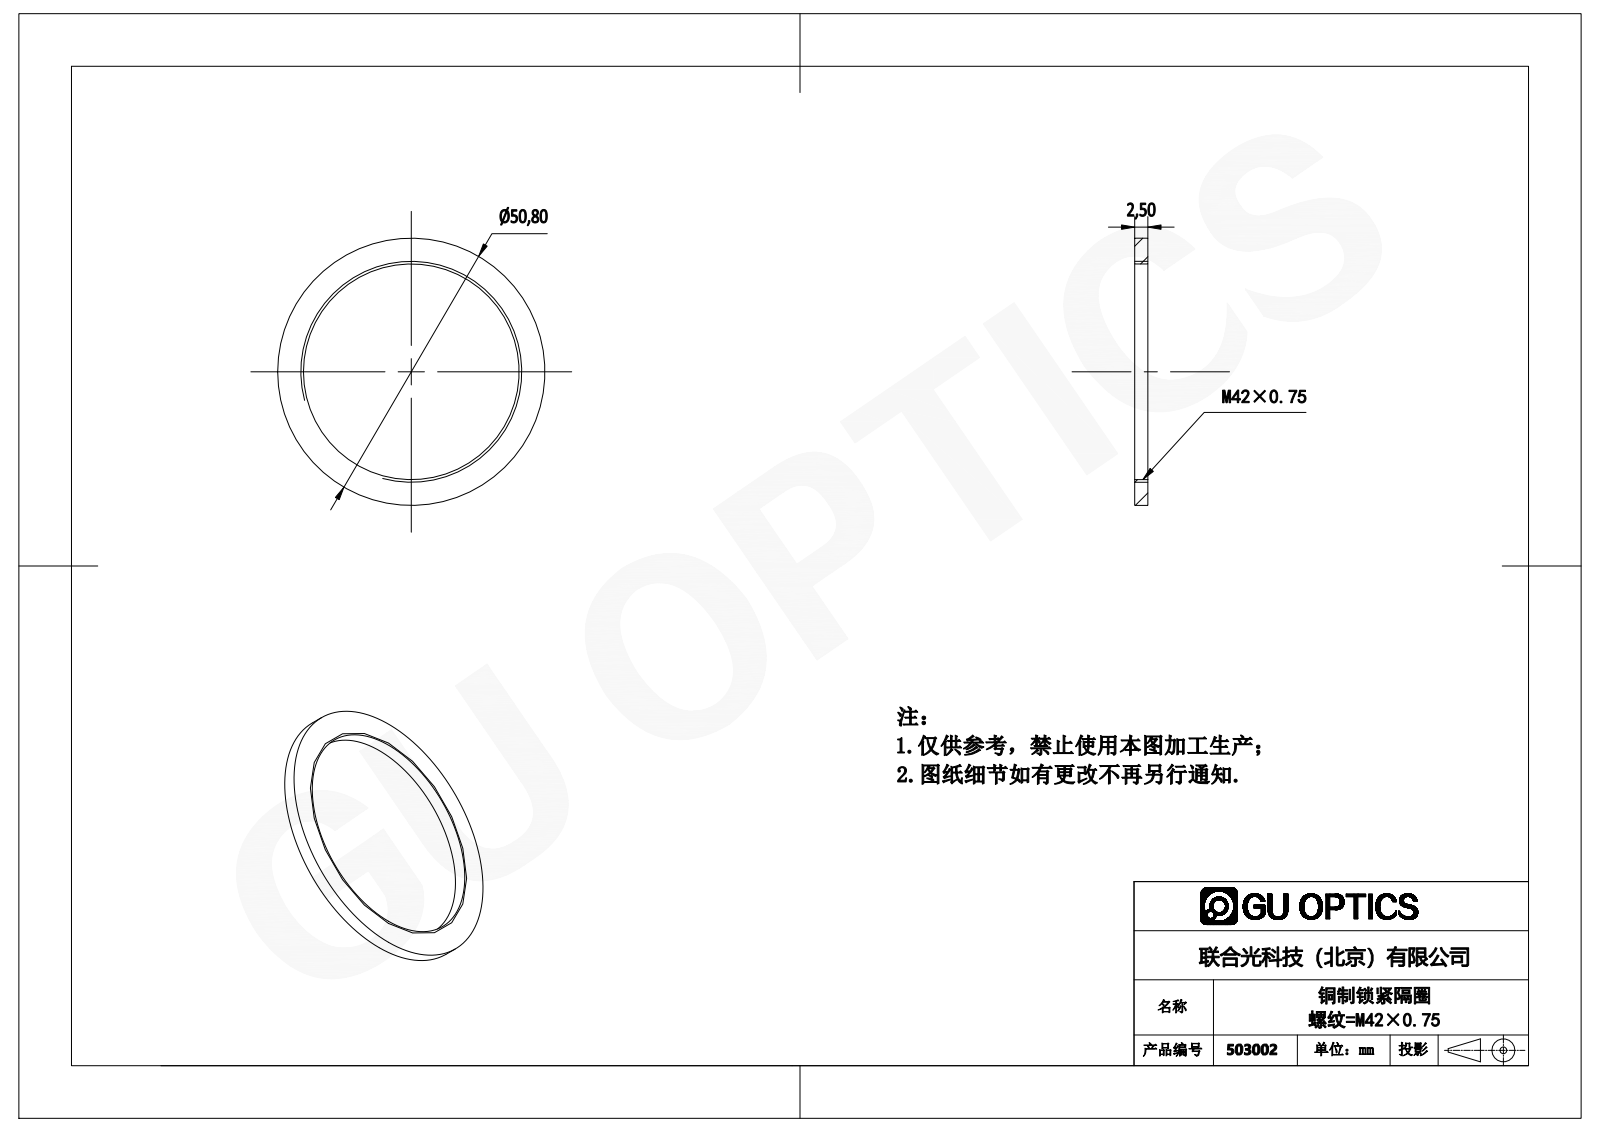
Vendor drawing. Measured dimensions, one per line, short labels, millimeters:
name: 511002
written by: SolidWorks 2016 (AUTOMOTIVE_DESIGN)
unit: mm
bodies: 1 solid, 6 faces (2 planar, 4 cylindrical, 0 other)
size: 50.8 × 50.8 × 2.5
volume: 1 766 mm³; area: 2 134 mm²
holes: 1× ⌀41
bosses: 1× ⌀50.8
face distances: 2.5
